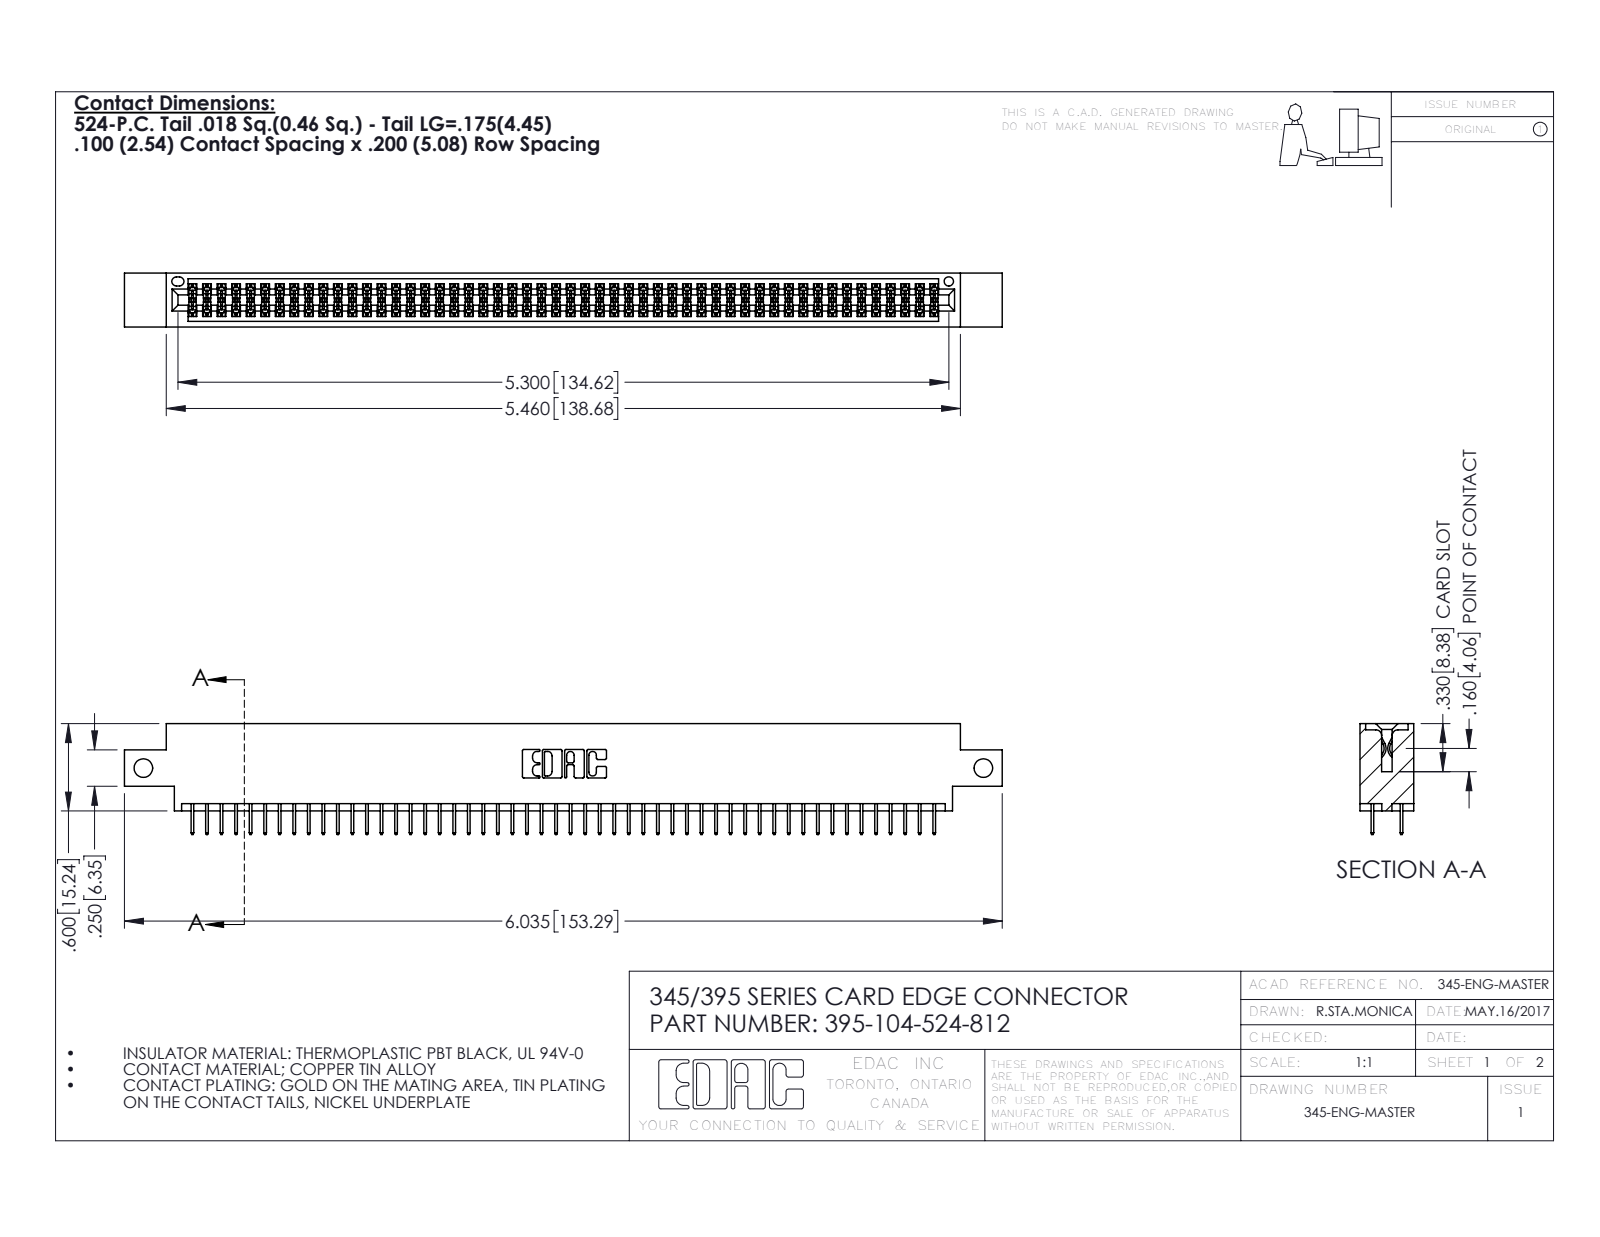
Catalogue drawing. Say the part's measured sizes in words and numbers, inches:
The part is named "345 Part_0.170 Offset - Side Mount; 345-292-001_345-293-124; 395-104-524-812". Its 3-D file was written by "SolidWorks 2016 (CONFIG_CONTROL_DESIGN)". It is 105 solids with 5746 faces: 4140 planar, 1606 cylindrical and 0 other. Overall it measures 6.035 by 0.762 by 0.37 inches. Its volume is 0.892 cubic inches and its surface area 33.18 square inches. Round holes: 2 of diameter 0.128, 1 of diameter 0.064. Partial cylindrical surfaces (rounded edges, fillets, slot ends): 156 of radius 0.006, 22 of radius 0.01, 6 of radius 0.007, 6 of radius 0.031, 3 of radius 0.026, 2 of radius 0.014, 2 of radius 0.019, 2 of radius 0.022. The main face-to-face distances are 0.072, 0.298, 0.37, 0.2, 0.098, 0.272, 0.025, 0.225, 0.175, 0.072. The hole center spacings are 5.775.
